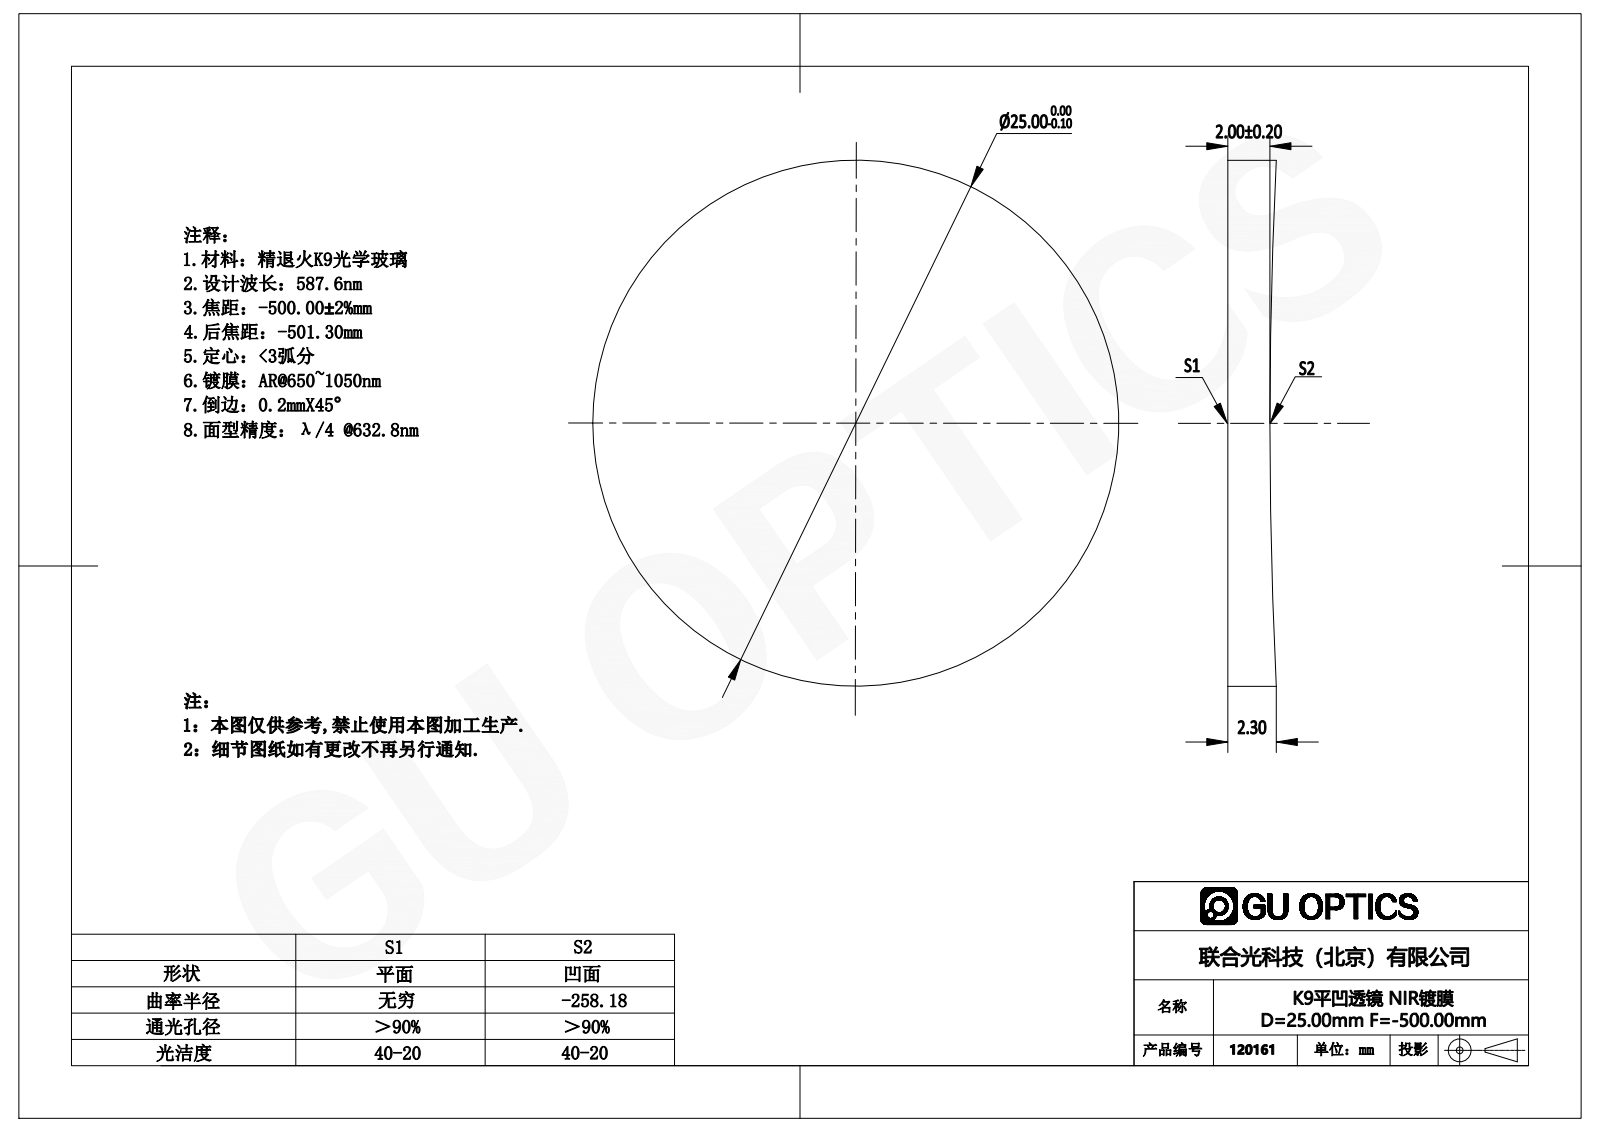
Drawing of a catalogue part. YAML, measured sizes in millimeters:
part_name: "120161"
step_written_by: "SolidWorks 2016 (AUTOMOTIVE_DESIGN)"
units: millimeters
bodies: {solids: 1, faces: 5, planar: 1, cylindrical: 2, other: 2}
overall_size: [25, 25, 2.3]
volume: 1056
surface_area: 1163
round_bosses_or_shafts:
  - {diameter: 25, count: 1}
